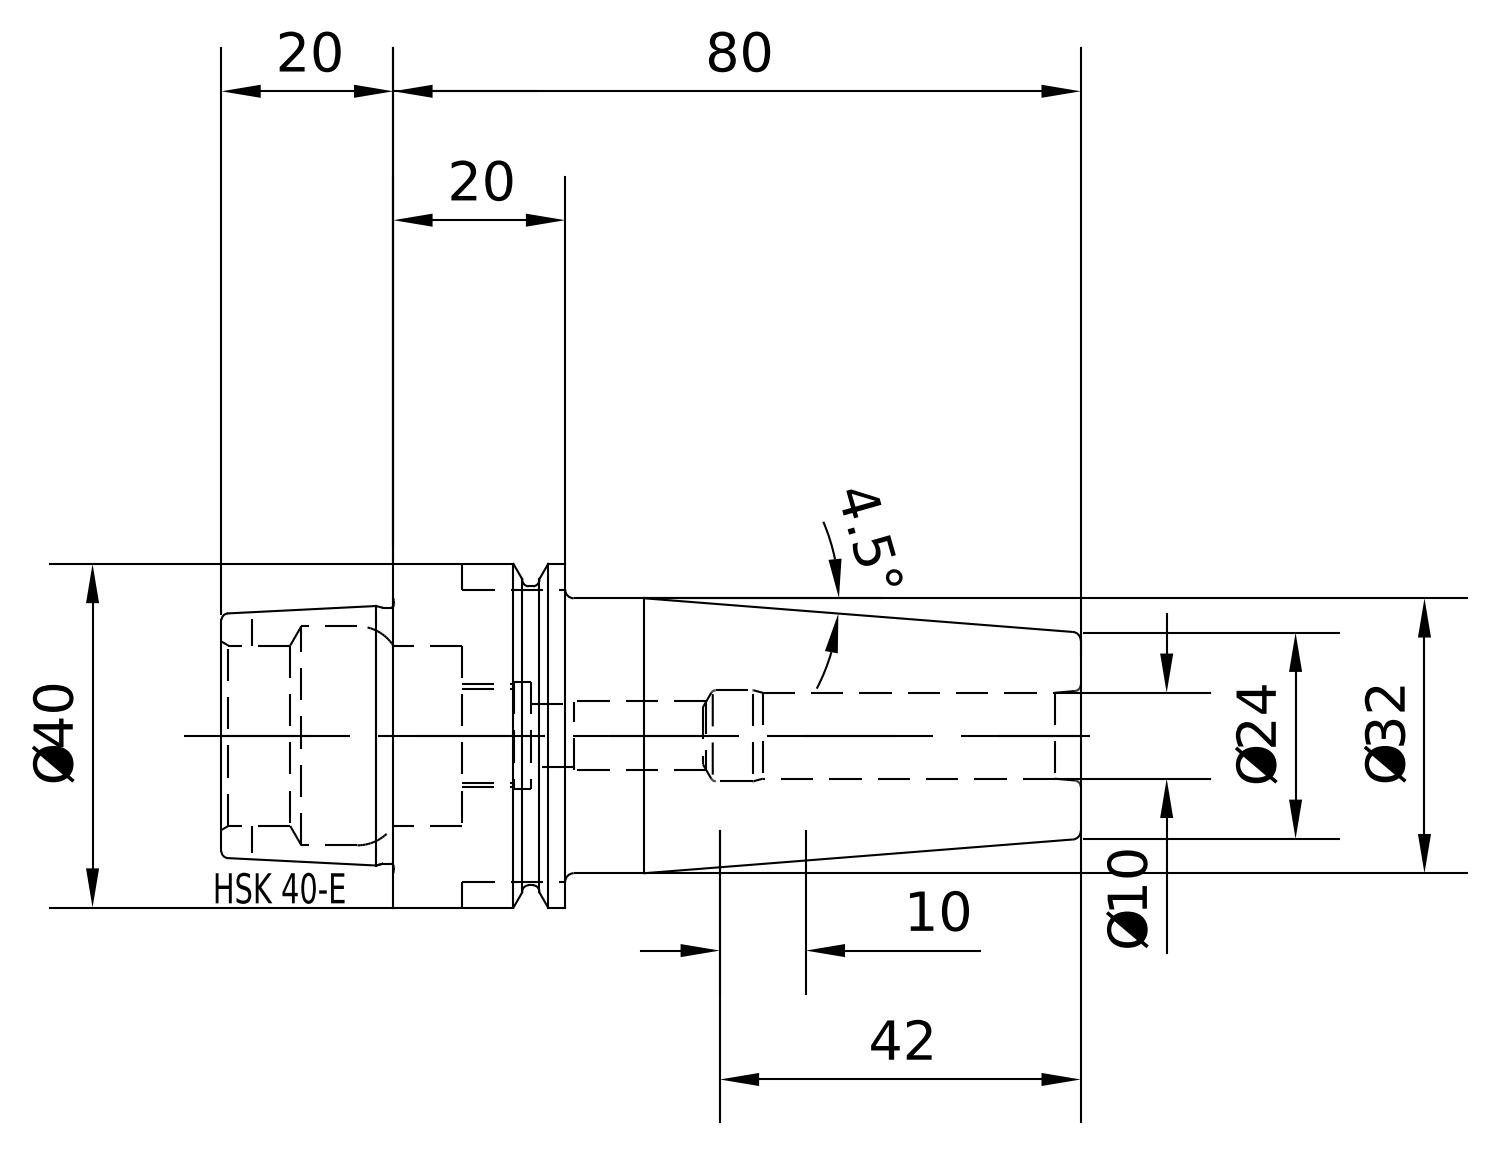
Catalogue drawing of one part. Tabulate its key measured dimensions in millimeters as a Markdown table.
| quantity | value |
| --- | --- |
| part name | E40-140-10 |
| STEP written by | PRO/ENGINEER BY PARAMETRIC TECHNOLOGY CORPORATION, 2010430 (CONFIG_CONTROL_DESIGN) |
| units | millimeters |
| bodies | 1 solid, 79 faces (9 planar, 24 cylindrical, 46 other) |
| overall size | 99.9 × 40 × 40 |
| volume | 61 107 mm³ |
| surface area | 15 887 mm² |
| round holes (diameter × count) | 10 × 1, 10.2 × 1, 12.22 × 1, 12.5 × 1, 21.04 × 1, 25.57 × 1 |
| round bosses / shafts (diameter × count) | 40 × 1, 34.75 × 1, 32 × 1, 29.81 × 1 |
| main face-to-face distances | 19.95, 80, 60.05, 19.9, 39.85, 99.9, 27.85, 7.95, 12, 72.05 |
